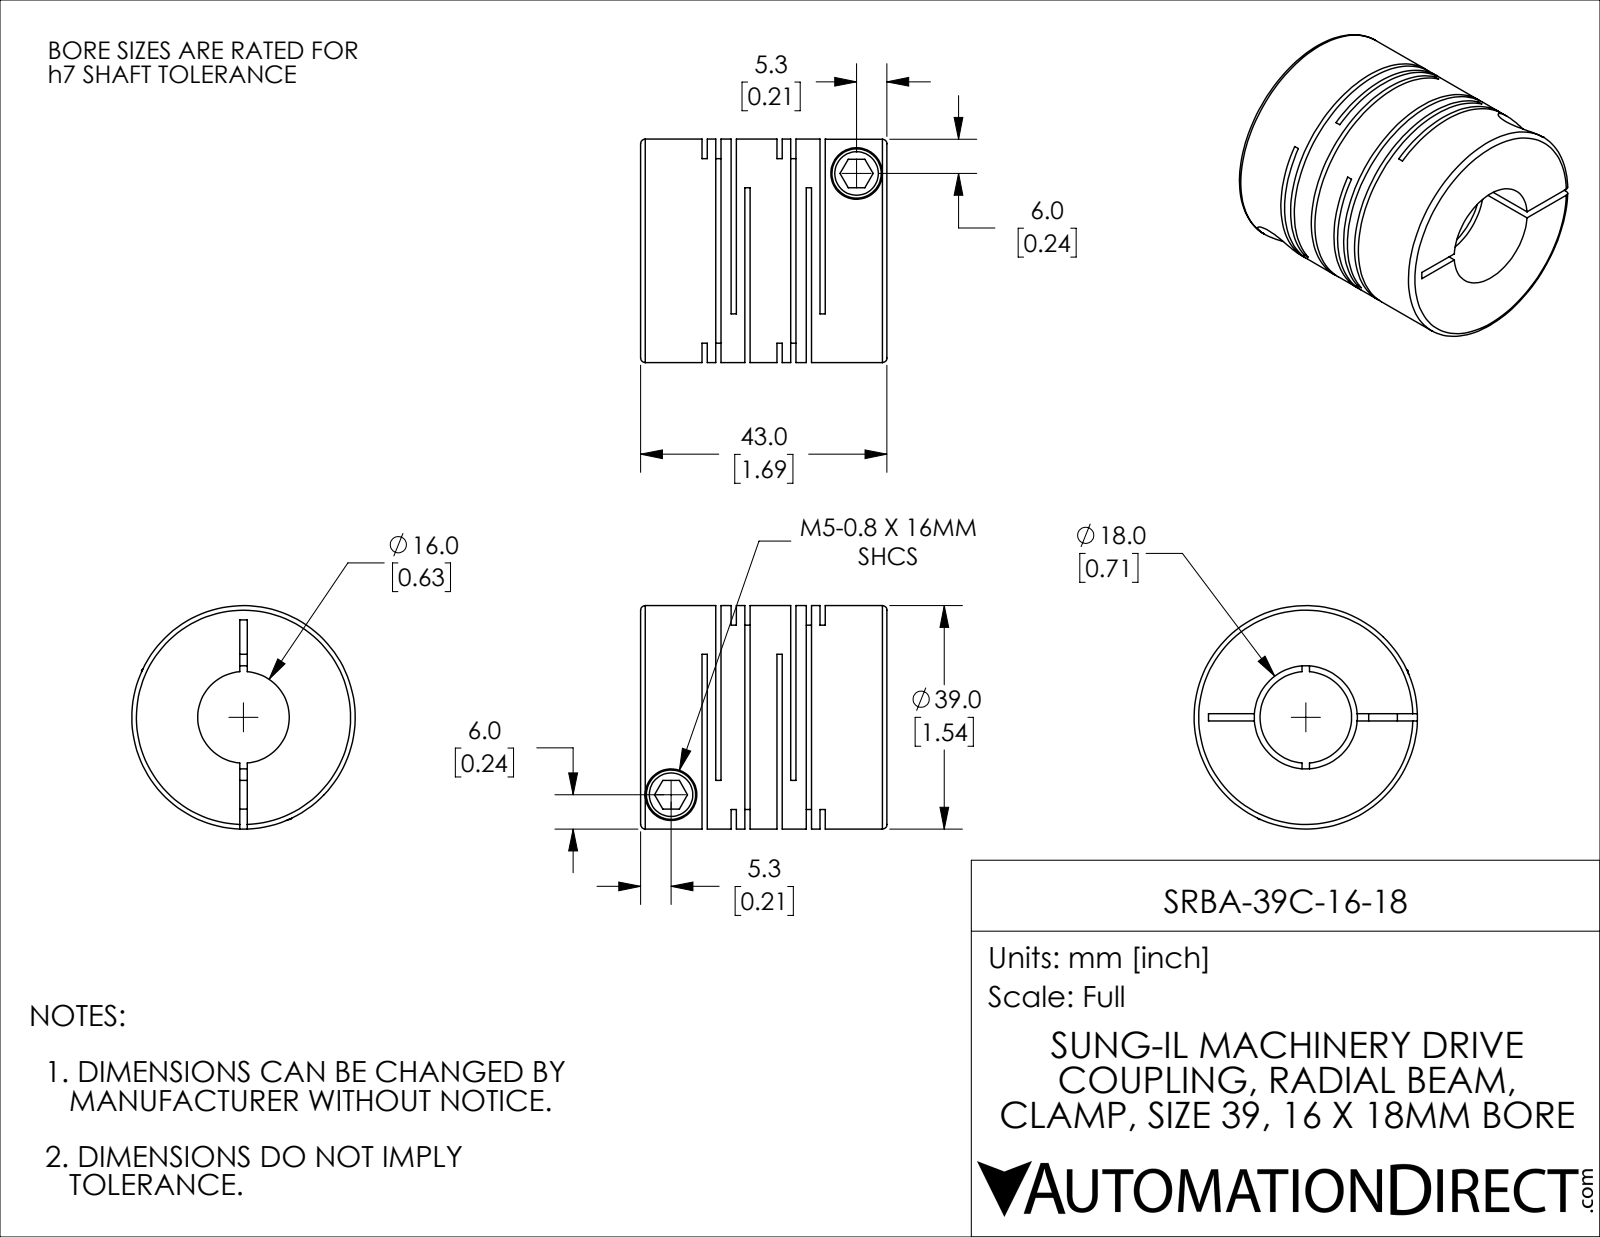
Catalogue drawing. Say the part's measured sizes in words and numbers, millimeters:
The part is named "SRBA-39C-16-18". Its 3-D file was written by "SolidWorks 2021 (CONFIG_CONTROL_DESIGN)". It is 1 solid with 114 faces: 60 planar, 42 cylindrical and 12 other. Overall it measures 43 by 39 by 39 millimeters. Its volume is 34 039 cubic millimeters and its surface area 22 203 square millimeters. Round holes: 2 of diameter 5, 2 of diameter 9, 1 of diameter 16, 1 of diameter 18. Round bosses or shafts: 2 of diameter 8.6, 1 of diameter 39. The main face-to-face distances are 13.1, 0.92, 2.4, 5.1, 10.7, 14.02, 18.2, 3.32, 1.48, 15.5.
